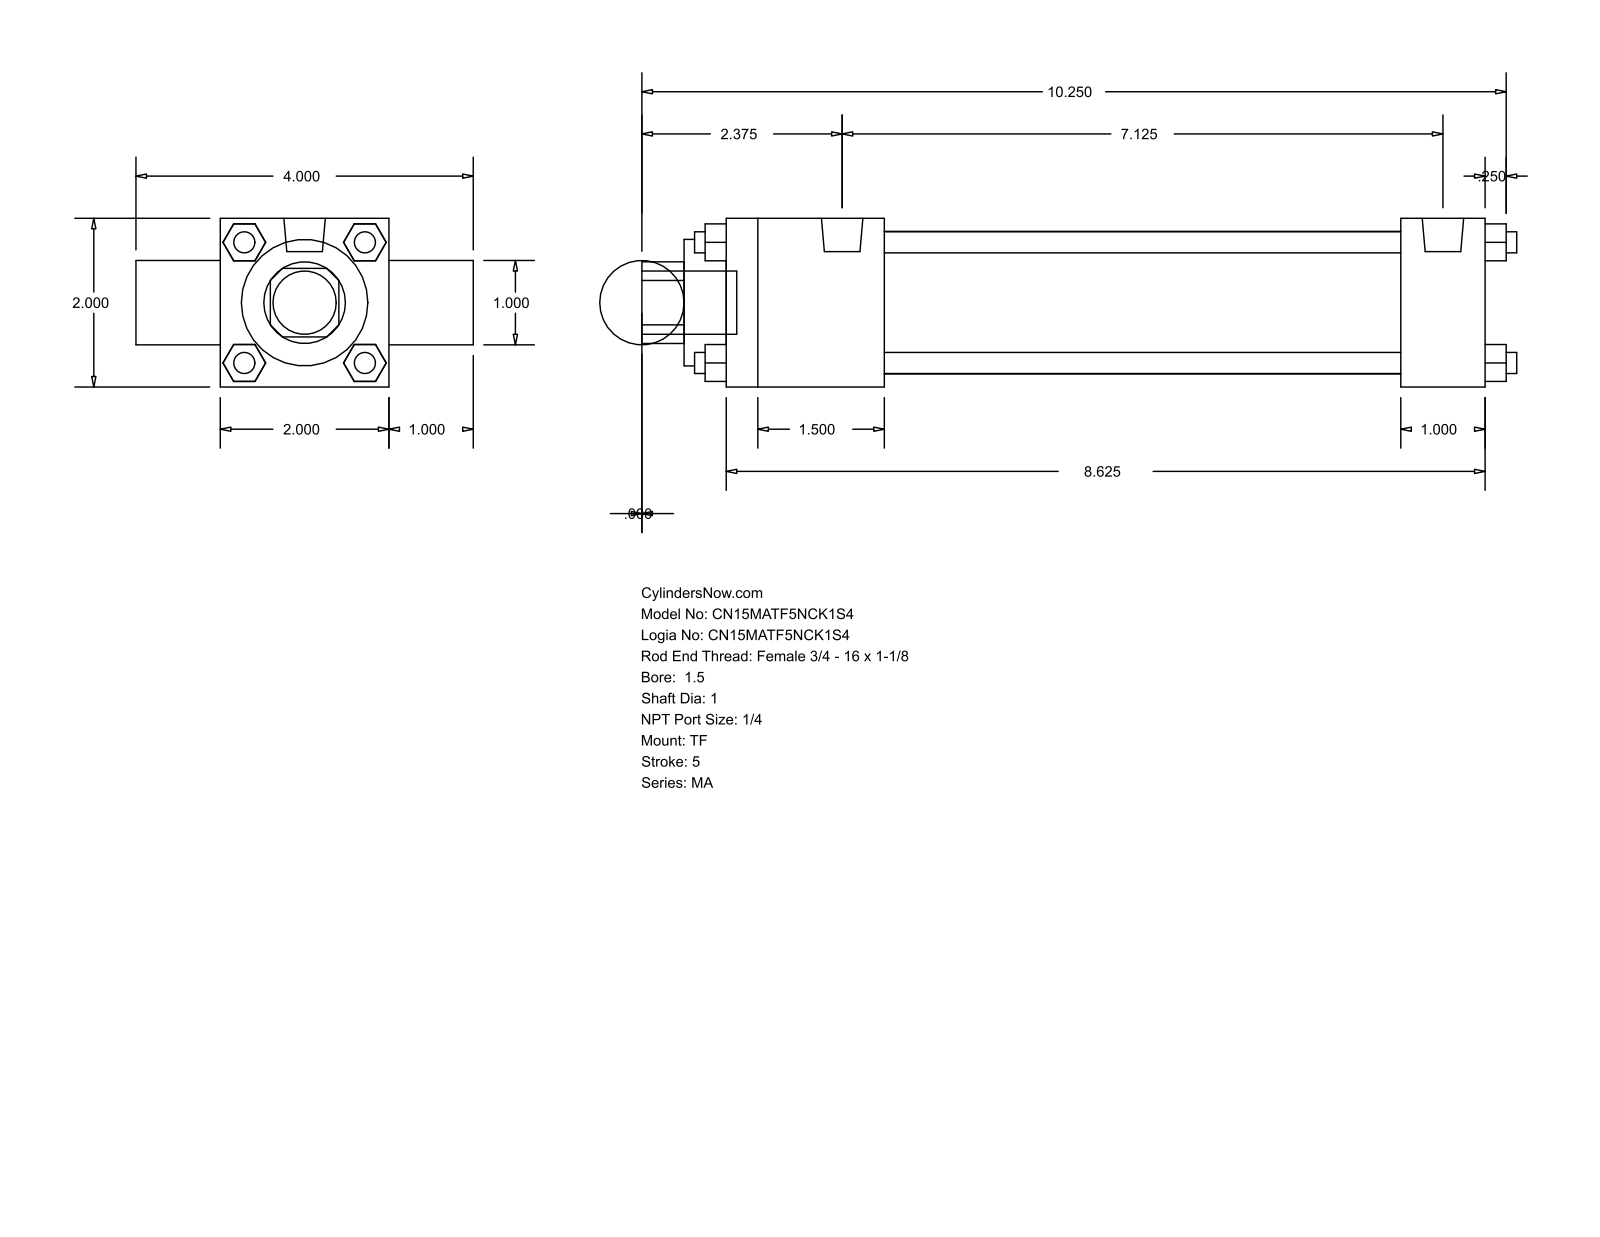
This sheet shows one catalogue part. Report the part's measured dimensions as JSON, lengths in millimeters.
{"part_name": "MA_TF__0150_1", "step_written_by": "GSSL Pune (CONFIG_CONTROL_DESIGN)", "units": "millimeters", "bodies": {"solids": 0, "faces": 120, "planar": 92, "cylindrical": 28, "other": 0}, "overall_size": [263.52, 101.6, 50.8], "round_holes": [[25.4, 2], [38.1, 1], [42.93, 1]], "round_bosses_or_shafts": [[6.35, 4], [7.94, 3], [12.49, 2], [19.05, 1]], "partial_cylinders_radius": [[12.29, 1]], "face_to_face_distances": [50.8, 25.4, 228.6, 76.2, 6.35, 47.63, 203.2, 155.57, 180.97, 241.3]}
